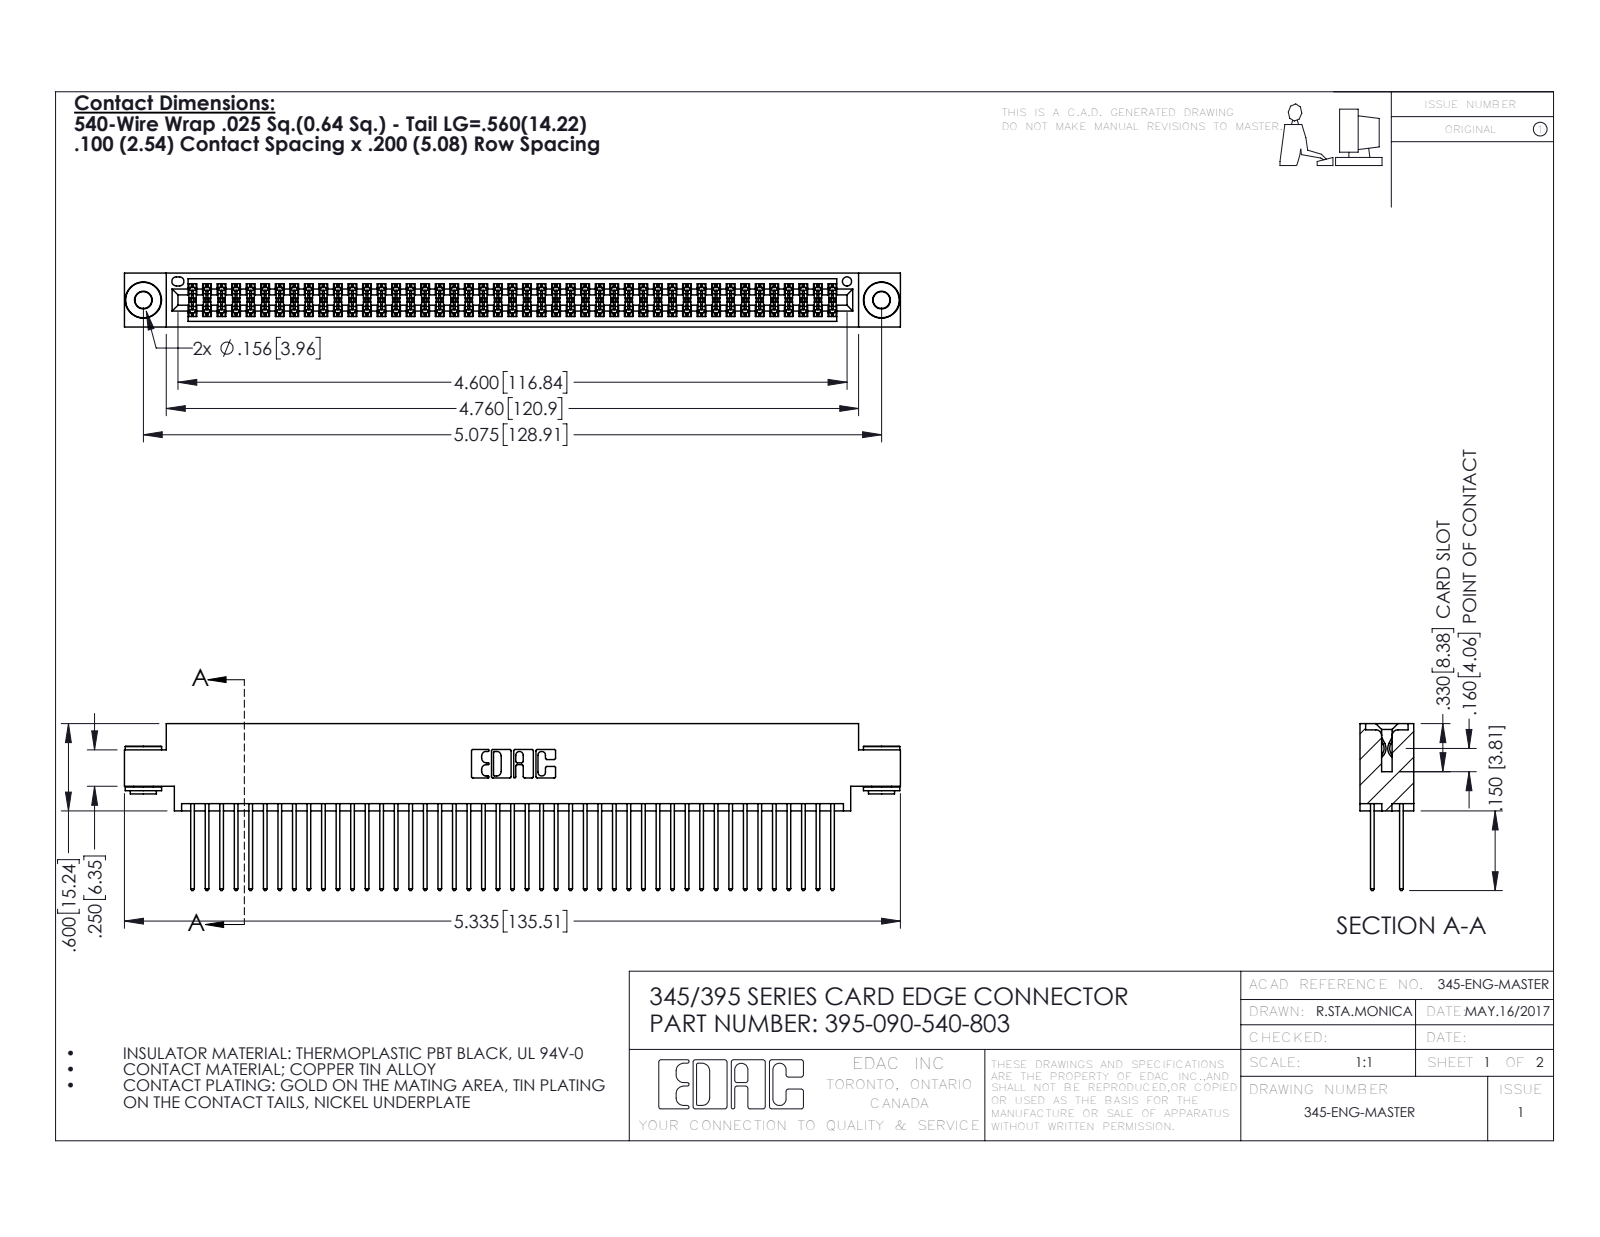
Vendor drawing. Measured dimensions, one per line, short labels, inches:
name: 345-292-001_345-293-140; 345 Part_0.170 Offset - 0.156 Dia-TH; 395-090-540-803; 345-250-002_345-250-002-102
written by: SolidWorks 2016 (CONFIG_CONTROL_DESIGN)
unit: in
bodies: 93 solids, 4668 faces (3064 planar, 1596 cylindrical, 8 other)
size: 5.335 × 1.147 × 0.37
volume: 0.82 in³; area: 33.87 in²
holes: 2× ⌀0.116, 2× ⌀0.156, 1× ⌀0.064
bosses: 2× ⌀0.25, 2× ⌀0.18, 2× ⌀0.136
rounds: 135× R0.006, 90× R0.01, 22× R0.01, 6× R0.007, 6× R0.031, 3× R0.026, 2× R0.014, 2× R0.019
face distances: 0.072, 0.298, 0.2, 0.098, 0.272, 0.025, 0.37, 0.225, 0.175, 0.149
hole spacings: 0.27, 4.839, 5.075
